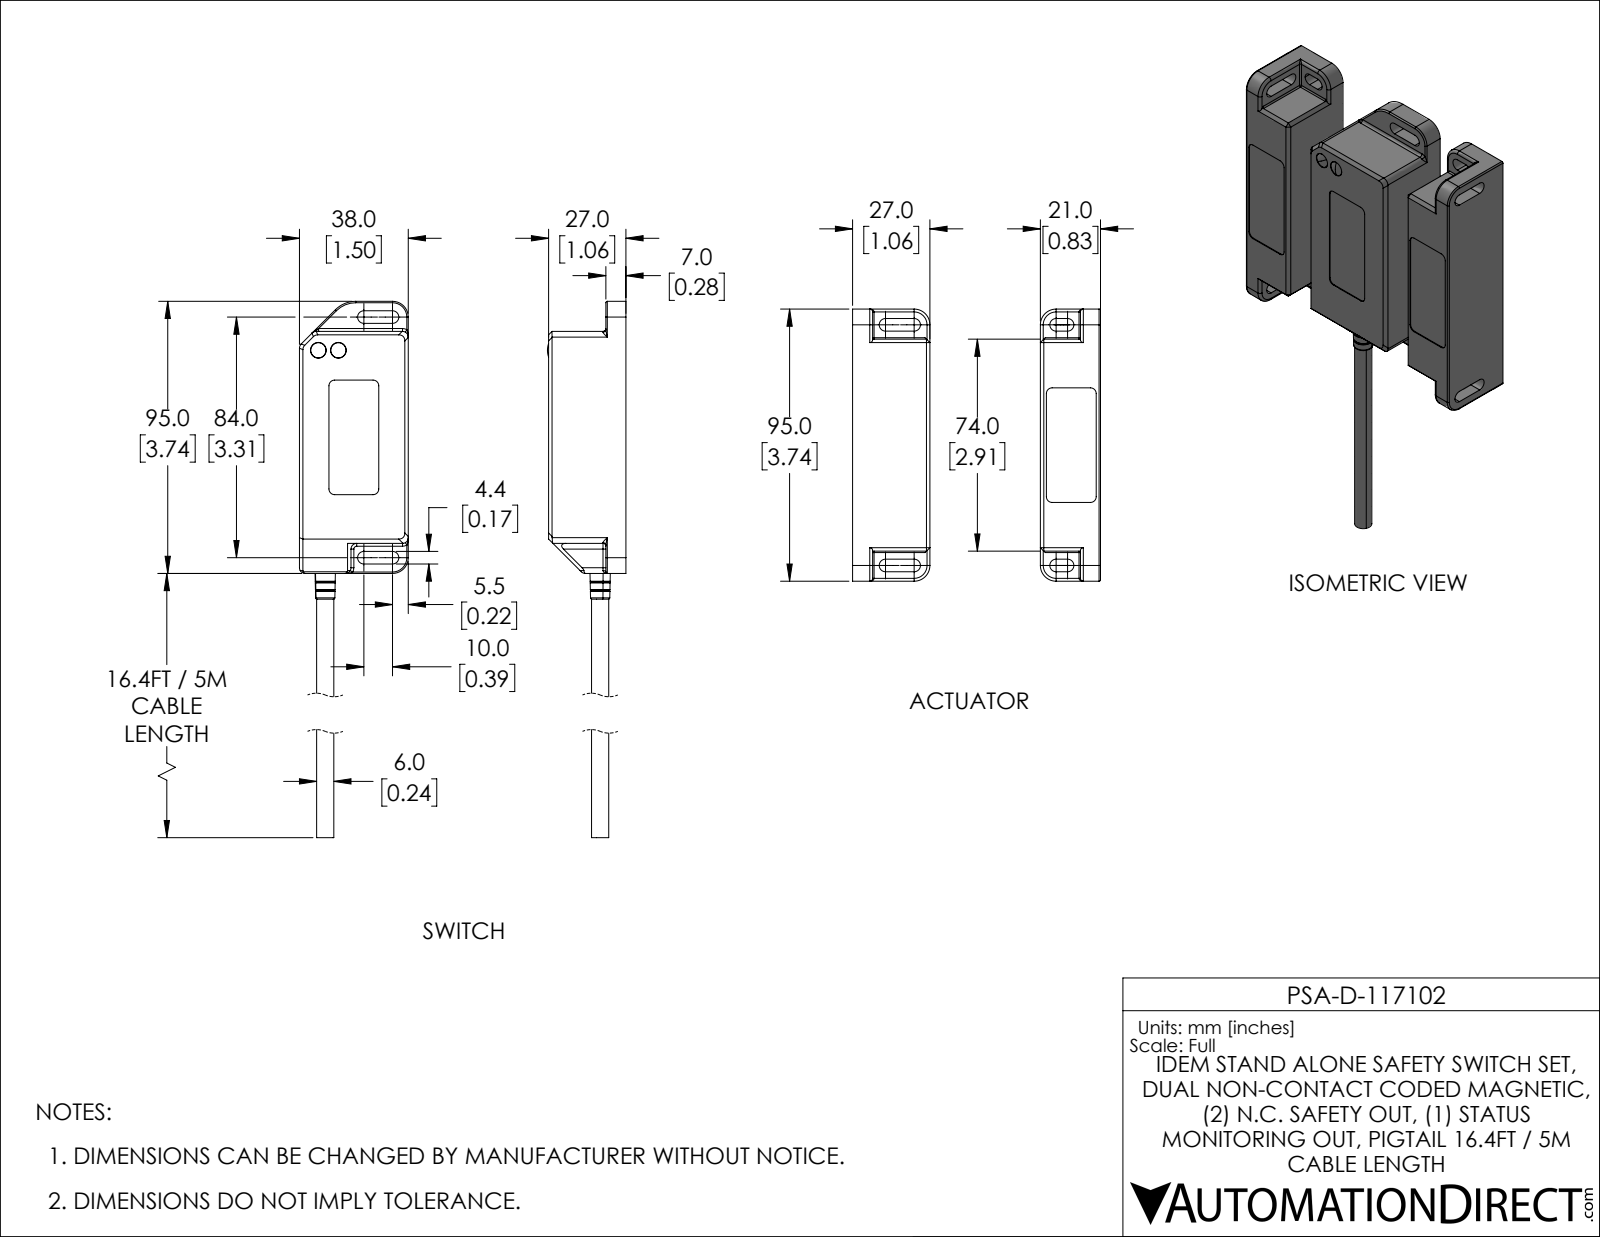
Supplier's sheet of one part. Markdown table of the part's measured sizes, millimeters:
| quantity | value |
| --- | --- |
| part name | 117-PSA-D |
| STEP written by | SolidWorks 2019 (AUTOMOTIVE_DESIGN) |
| units | millimeters |
| bodies | 3 solids, 1348 faces (655 planar, 344 cylindrical, 349 other) |
| overall size | 180.1 × 100 × 27.4 |
| volume | 66 550 mm³ |
| surface area | 61 080 mm² |
| round holes (diameter × count) | 2.9 × 2, 5.5 × 2, 8.2 × 1 |
| round bosses / shafts (diameter × count) | 5 × 3, 2 × 3, 5.3 × 2, 4.5 × 2, 8.6 × 1, 7.6 × 1, 7.1 × 1, 6 × 1 |
| partial cylindrical surfaces (radius × count) | 0.5 × 113, 2 × 22, 0.3 × 16, 2.2 × 16, 1 × 15, 0.2 × 8, 5.5 × 8, 3 × 4 |
| main face-to-face distances | 2, 48, 79, 31, 12, 19, 67, 69, 24.8, 1.6 |
| hole center spacings | 7 |
